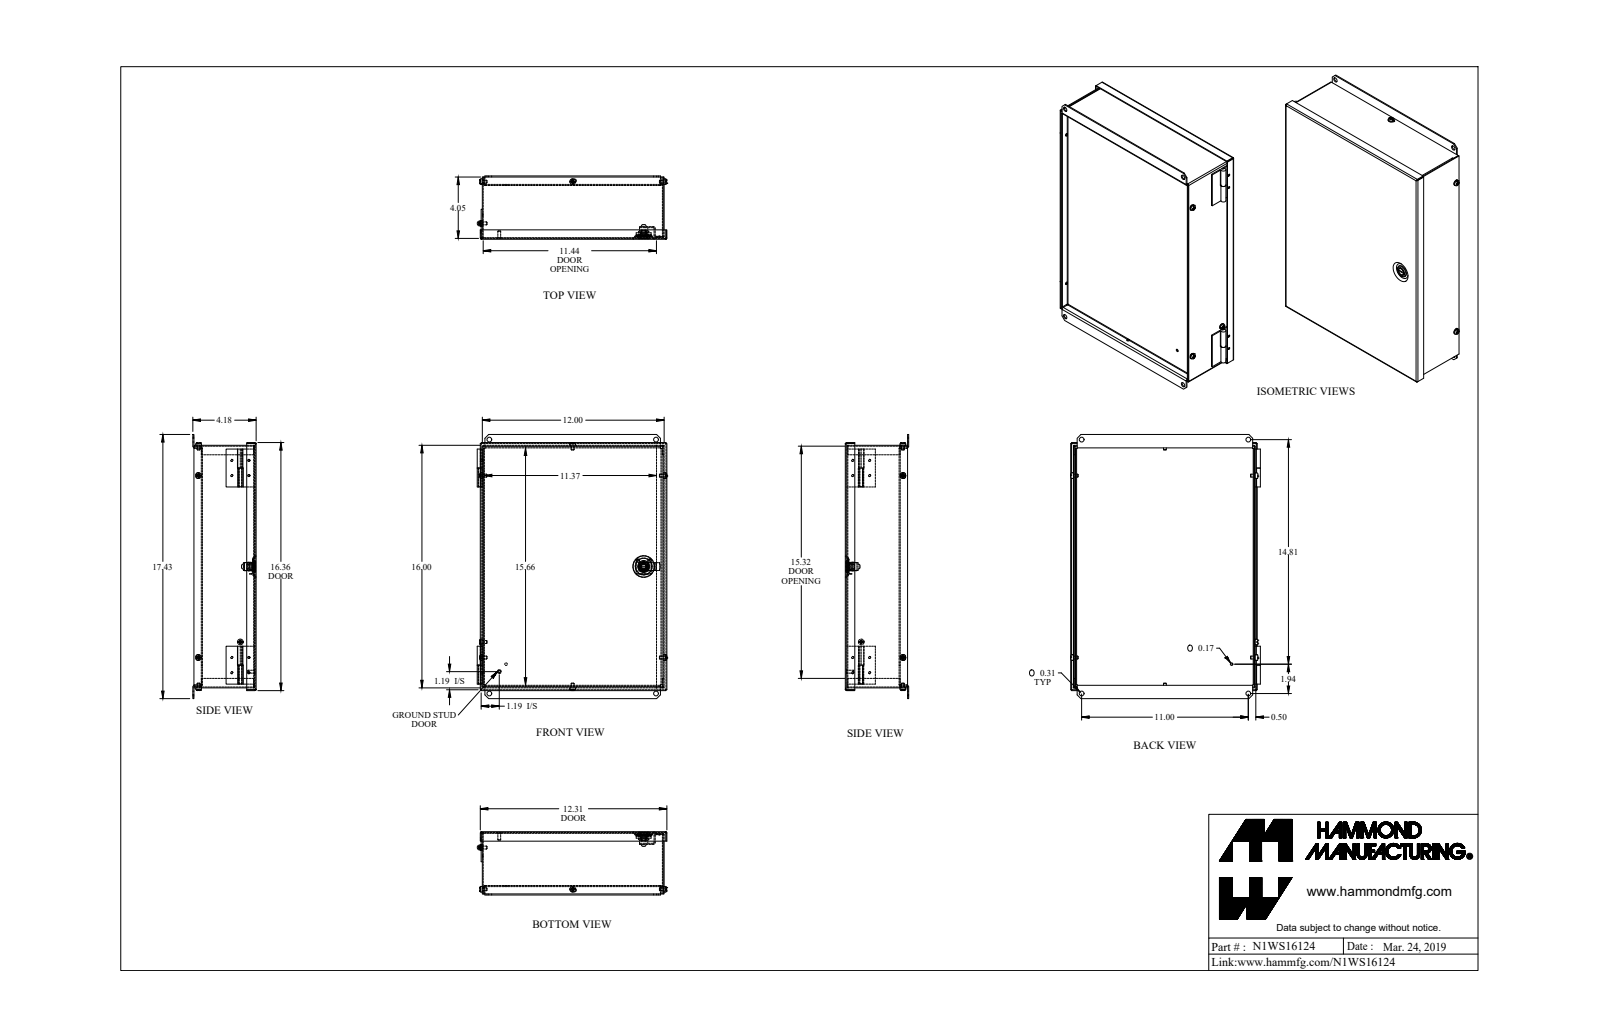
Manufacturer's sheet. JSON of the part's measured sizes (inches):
{"part_name": "N1WS16124", "step_written_by": "SolidWorks 2018 (AUTOMOTIVE_DESIGN)", "units": "inches", "bodies": {"solids": 18, "faces": 634, "planar": 345, "cylindrical": 218, "other": 71}, "overall_size": [17.425, 12.519, 4.179], "volume_in3": 44.62, "surface_area_in2": 1447, "round_holes": [[0.14, 8], [0.17, 5], [0.312, 4], [0.187, 1], [0.319, 1], [0.476, 1]], "round_bosses_or_shafts": [[0.128, 8], [0.375, 5], [0.19, 5], [0.787, 1], [0.547, 1], [0.472, 1], [0.469, 1], [0.366, 1]], "partial_cylinders_radius": [[0.029, 9], [0.086, 9], [0.036, 8], [0.108, 6], [0.109, 6], [0.012, 4], [0.1, 4], [0.079, 2]], "face_to_face_distances": [0.057, 0.072, 0.057, 3.564, 3.621, 3.492, 3.549, 11.943, 15.943, 11.886], "hole_center_spacings": [1, 1.119, 1.501, 13, 13.048, 12, 2.195, 2.412]}
